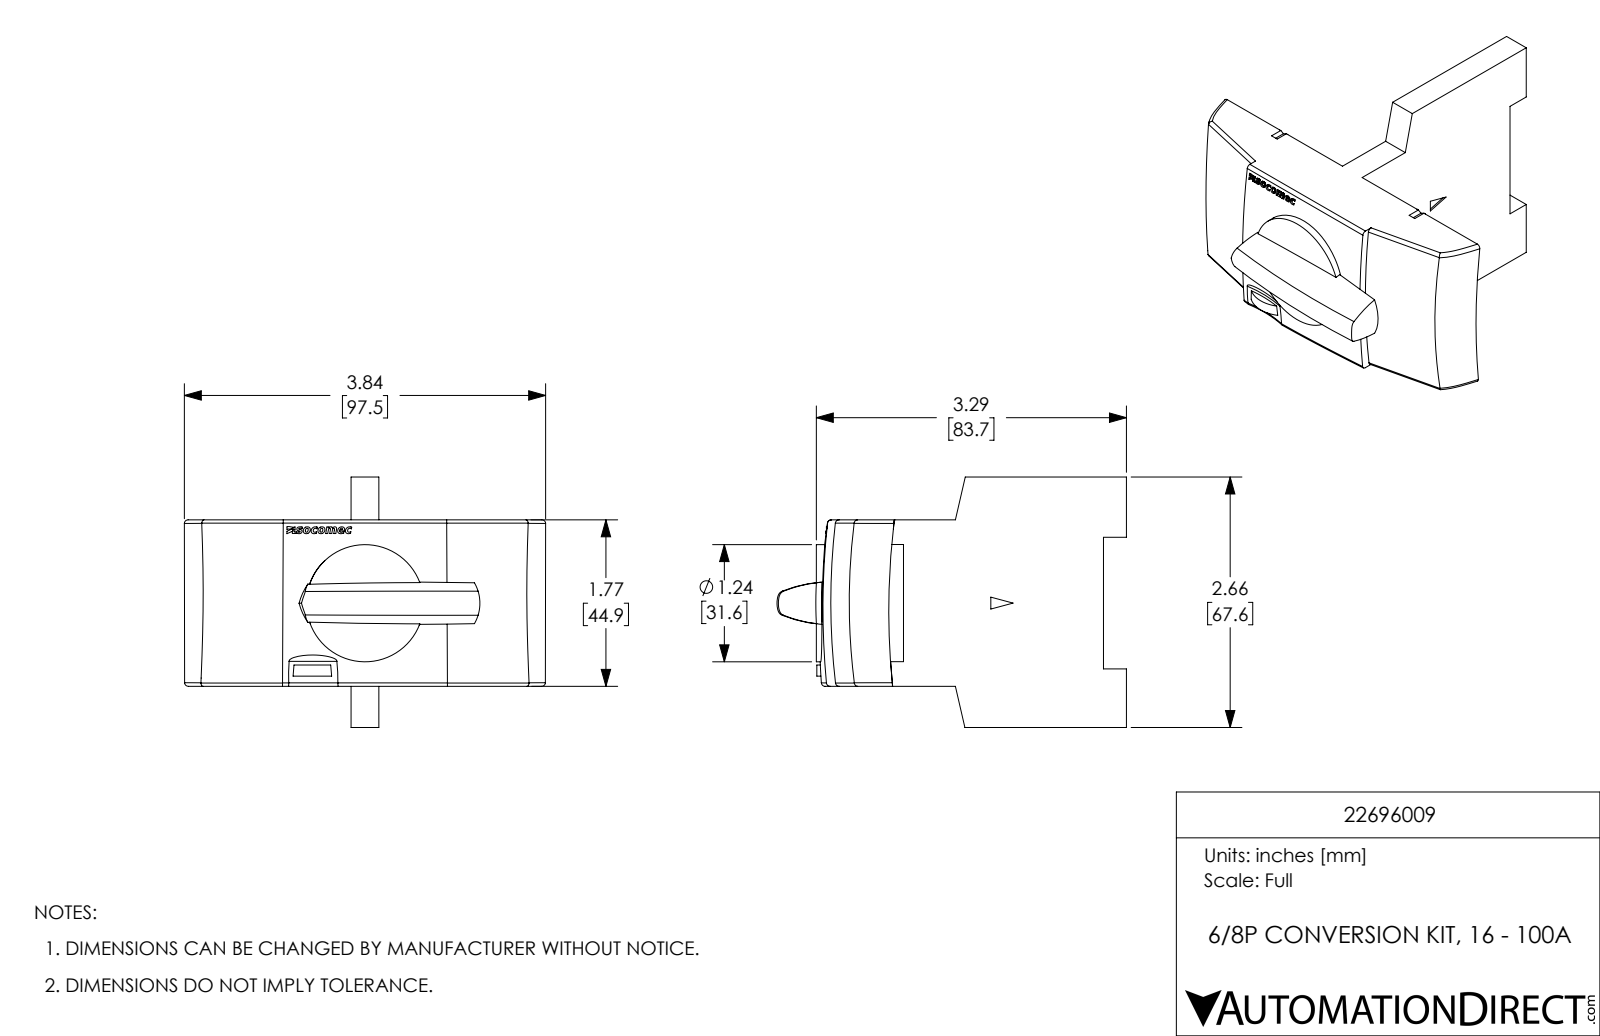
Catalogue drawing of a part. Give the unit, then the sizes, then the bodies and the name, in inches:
Units: inches
Overall size (bounding box): 3.838 × 3.713 × 2.659
Round holes (diameter × count): ⌀0.74 ×1, ⌀1.244 ×1
Round bosses / shafts (diameter × count): ⌀1.244 ×3, ⌀0.079 ×1
Partial cylindrical surfaces — rounded edges, fillets, slot ends (radius × count): R0.039 ×4, R0.37 ×3, R7.559 ×2
Main face-to-face distances: 0.295, 1.768, 0.87, 0.717, 0.154, 0.734, 0.018, 0.136, 0.926, 0.209
Volume: 6.29 in³ · Surface area: 41.11 in²
Bodies: 3 solids, 197 faces (112 planar, 25 cylindrical, 60 other)
Part name (STEP PRODUCT): 22696009
STEP written by: SolidWorks 2017 (AUTOMOTIVE_DESIGN)
